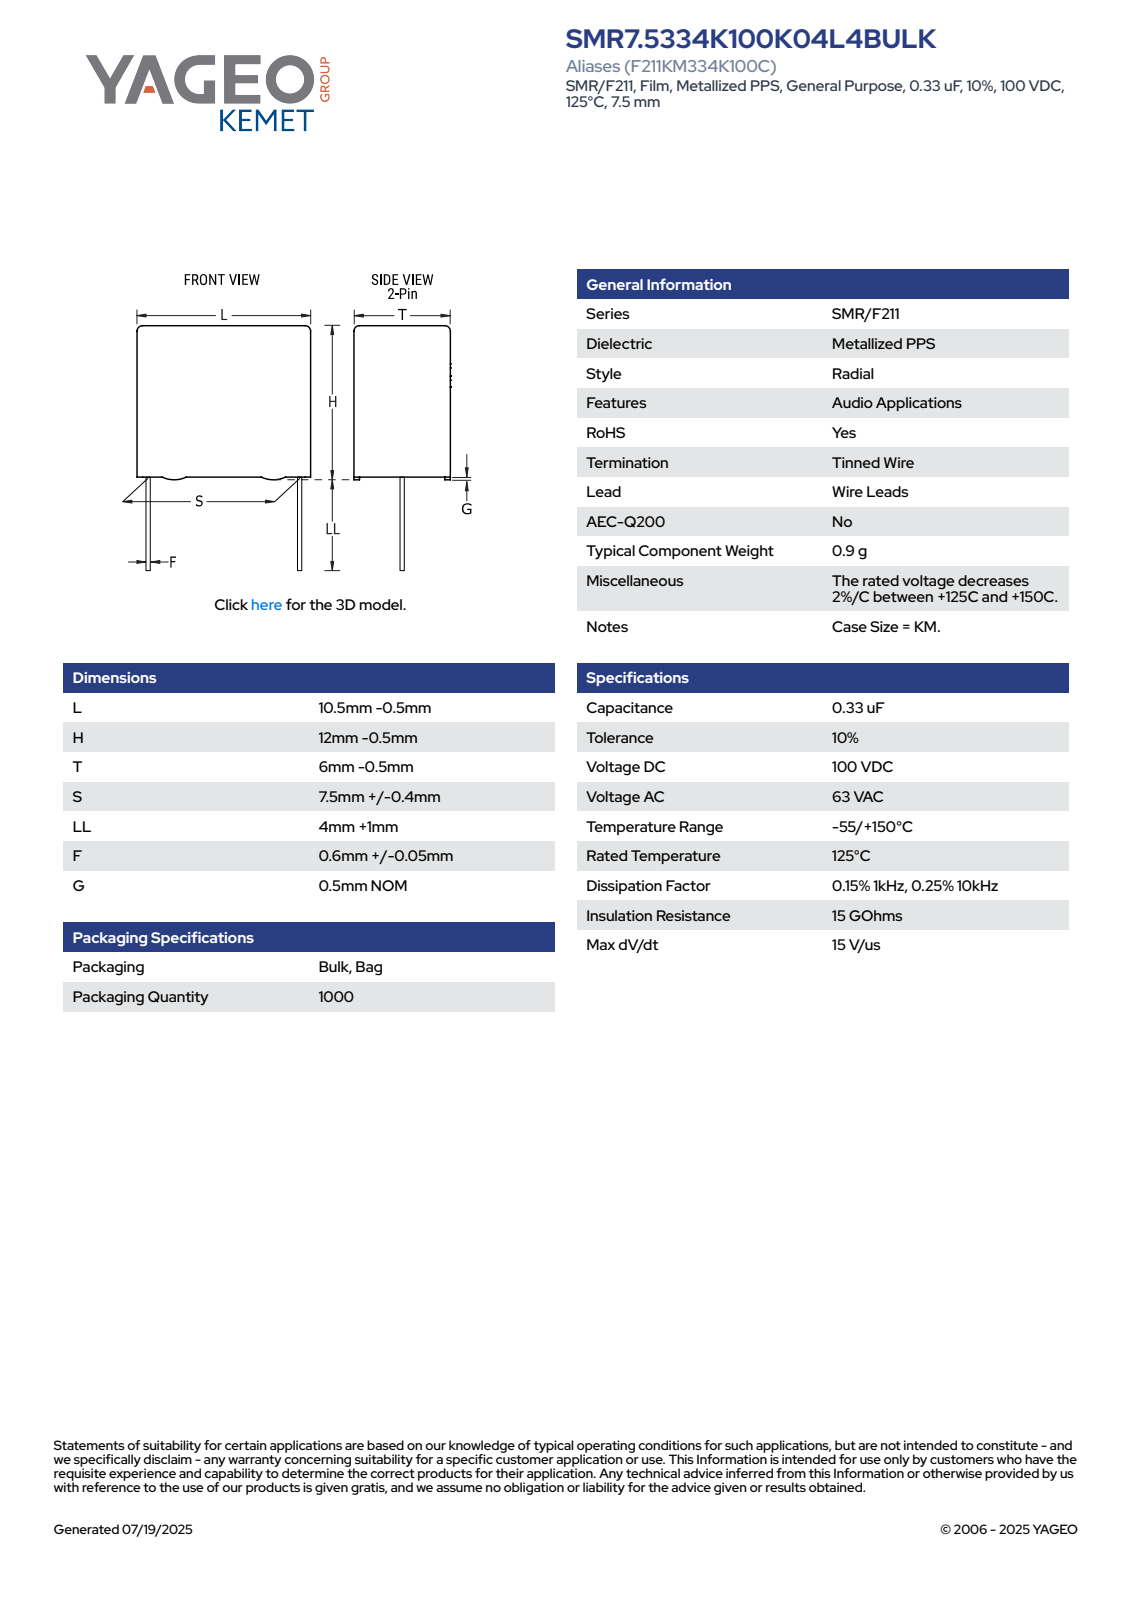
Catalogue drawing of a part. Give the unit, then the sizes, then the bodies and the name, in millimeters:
Units: millimetres
Overall size (bounding box): 16.5 × 10 × 5.5
Round bosses / shafts (diameter × count): ⌀0.65 ×2
Partial cylindrical surfaces — rounded edges, fillets, slot ends (radius × count): R0.5 ×4
Main face-to-face distances: 5.5, 10, 11, 5.19, 0.31, 0.5, 11.5, 4.88, 5, 16.5
Volume: 608 mm³ · Surface area: 485 mm²
Bodies: 4 solids, 89 faces (81 planar, 8 cylindrical, 0 other)
Part name (STEP PRODUCT): CFR_RBG_10.5X12X6_L10H11.5T5.5S7.5LL5F0.65G0.5
STEP written by: SolidWorks 2021 (AUTOMOTIVE_DESIGN)
